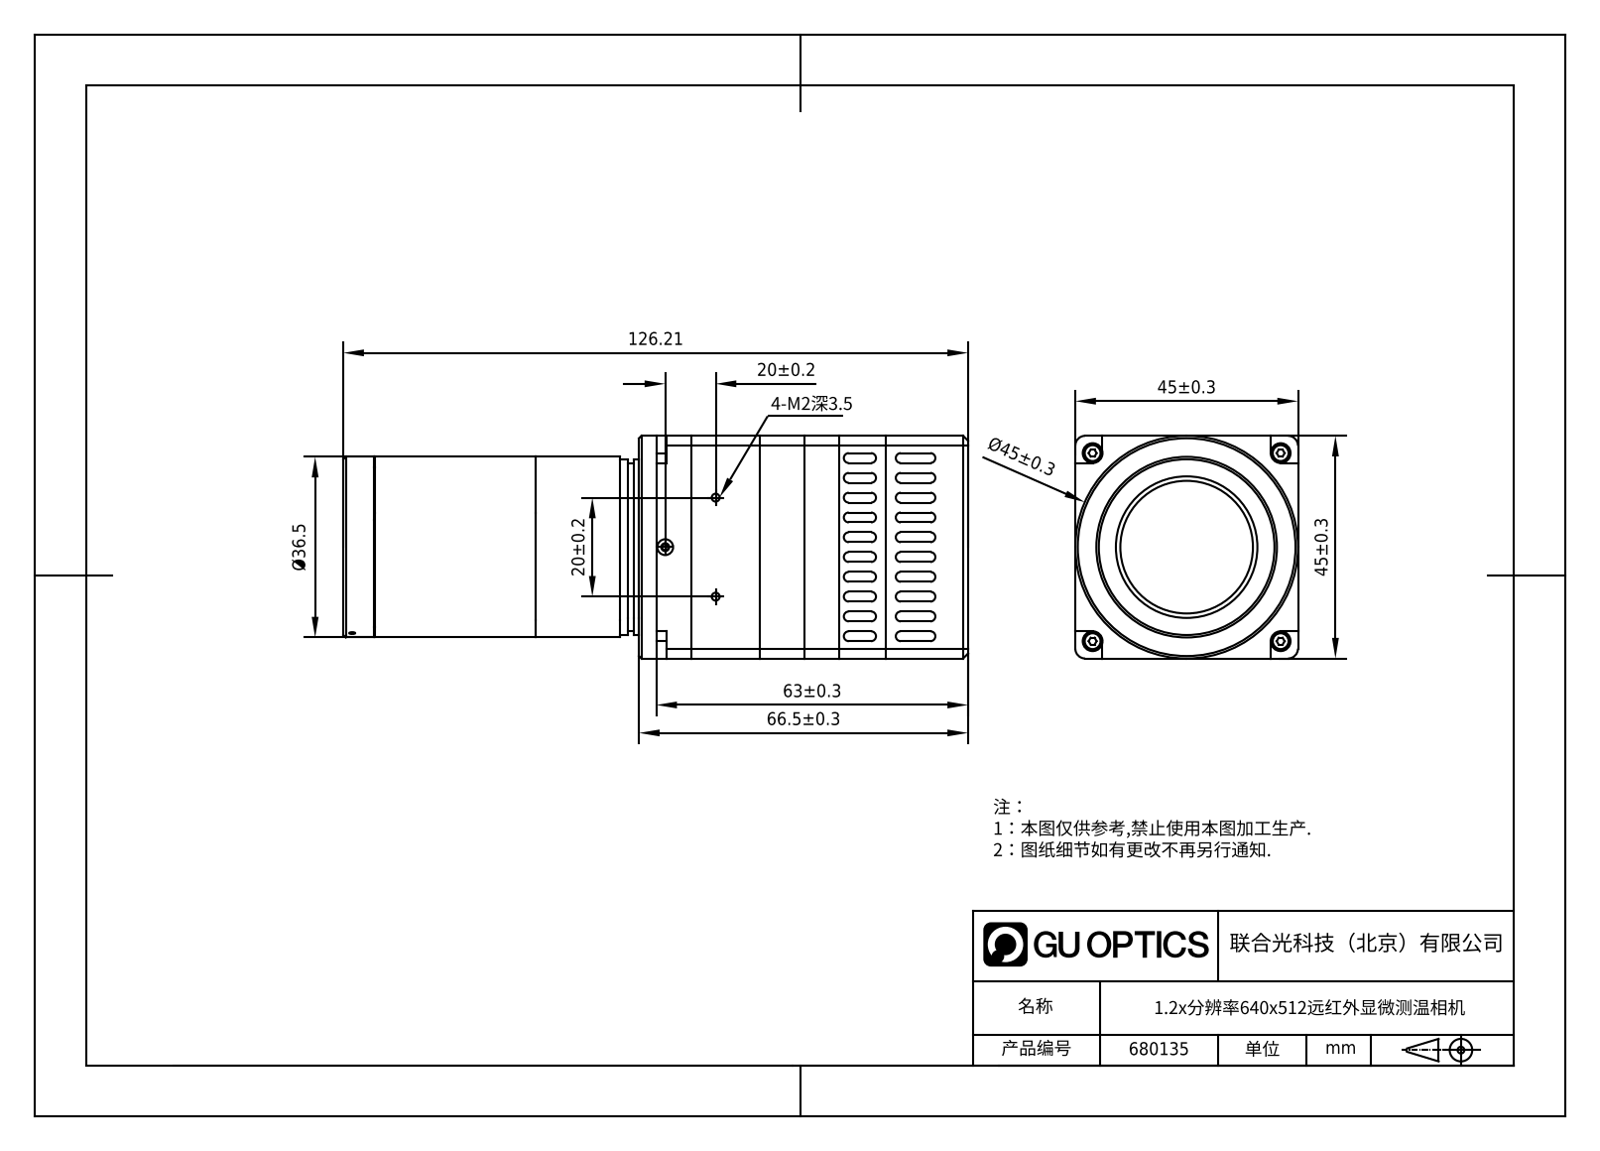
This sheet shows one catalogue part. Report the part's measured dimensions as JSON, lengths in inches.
{"part_name": "680135", "step_written_by": "SolidWorks 2020 (CONFIG_CONTROL_DESIGN)", "units": "inches", "bodies": {"solids": 0, "faces": 3008, "planar": 1967, "cylindrical": 908, "other": 133}, "overall_size": [4.971, 1.772, 1.772], "round_holes": [[0.063, 10], [0.026, 6], [0.049, 6], [0.067, 6], [0.028, 4], [0.029, 4], [0.043, 4], [0.059, 4], [0.087, 4], [0.126, 4], [0.138, 4], [0.157, 4]], "round_bosses_or_shafts": [[0.028, 37], [0.018, 36], [0.079, 11], [0.071, 10], [0.063, 7], [0.142, 4], [0.118, 4], [0.087, 4]], "partial_cylinders_radius": [[0.004, 160], [0.039, 97], [0.059, 58], [0.079, 24], [0.02, 18], [0.005, 12], [0.012, 10], [0.021, 8]], "face_to_face_distances": [1, 0.276, 1.772, 0.063, 0.366, 0.067, 1.063, 1.654, 0.63, 0.039], "hole_center_spacings": [1.496, 0.151, 0.157, 0.252, 0.402, 0.562, 0.787, 0.953]}
